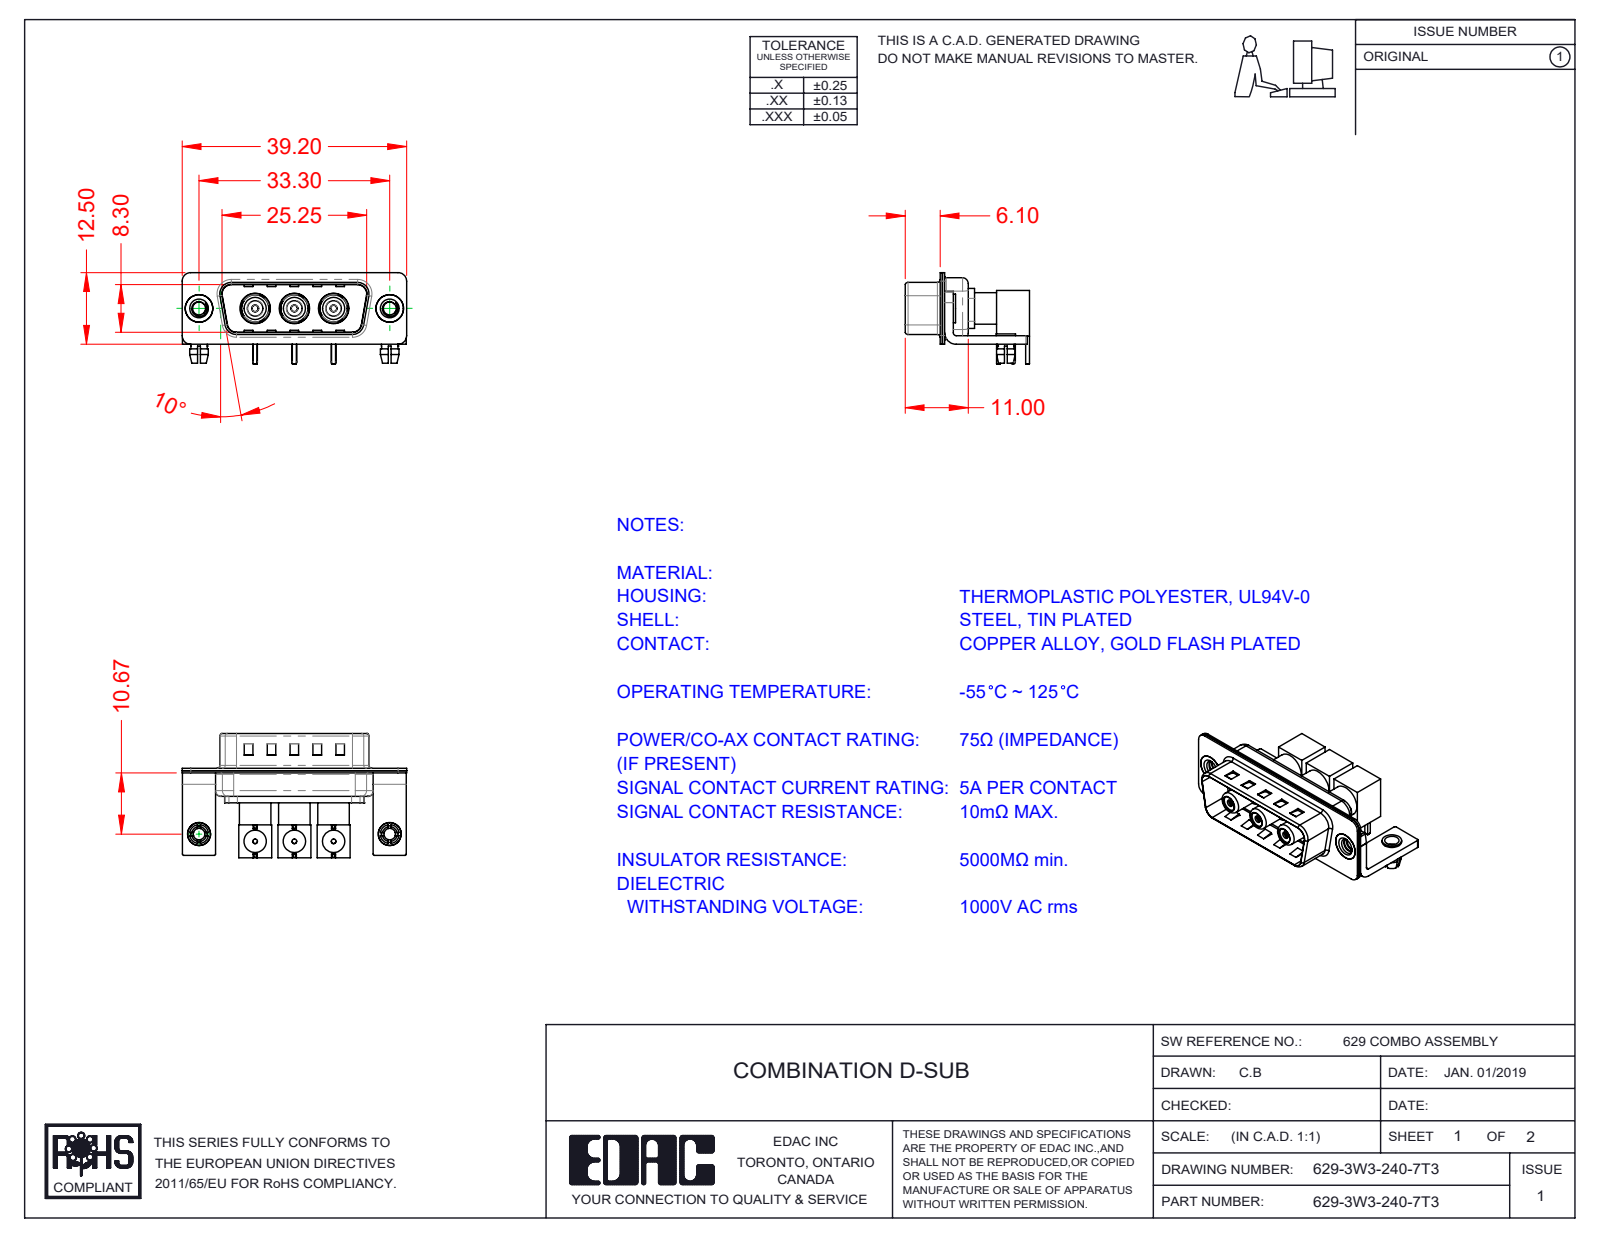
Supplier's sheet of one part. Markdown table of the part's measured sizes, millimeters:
| quantity | value |
| --- | --- |
| part name | Co-Ax Jack_RA PC Tail; Socket_RA; Co-Ax Jack Assy_RA; Insulator Socket (+8 more) |
| STEP written by | SolidWorks 2020 (CONFIG_CONTROL_DESIGN) |
| units | millimeters |
| bodies | 30 solids, 928 faces (378 planar, 384 cylindrical, 166 other) |
| overall size | 39.2 × 21.71 × 16 |
| volume | 3 001 mm³ |
| surface area | 8 320 mm² |
| round holes (diameter × count) | 2.5 × 5, 0.8 × 3, 1.1 × 3, 1.2 × 3, 1.5 × 3, 1.6 × 3, 2.7 × 3, 3.1 × 3, 3.4 × 3, 3.9 × 3, 4.1 × 3, 4.85 × 3 |
| round bosses / shafts (diameter × count) | 0.8 × 6, 4 × 5, 3.3 × 5, 2.9 × 5, 5.5 × 3, 5.2 × 3, 4.8 × 3, 4.73 × 3 |
| partial cylindrical surfaces (radius × count) | 0.25 × 16, 1.5 × 16, 2 × 13, 0.5 × 9, 1.6 × 8, 0.6 × 4, 0.65 × 4, 0.9 × 4 |
| main face-to-face distances | 0.4, 0.8, 1.5, 5.75, 9.5, 1.4, 9.1, 1.1, 0.35, 6.85 |
| hole center spacings | 6.85, 13.7, 9.88, 16.7, 23.53, 9.8, 16.65, 23.5 |
